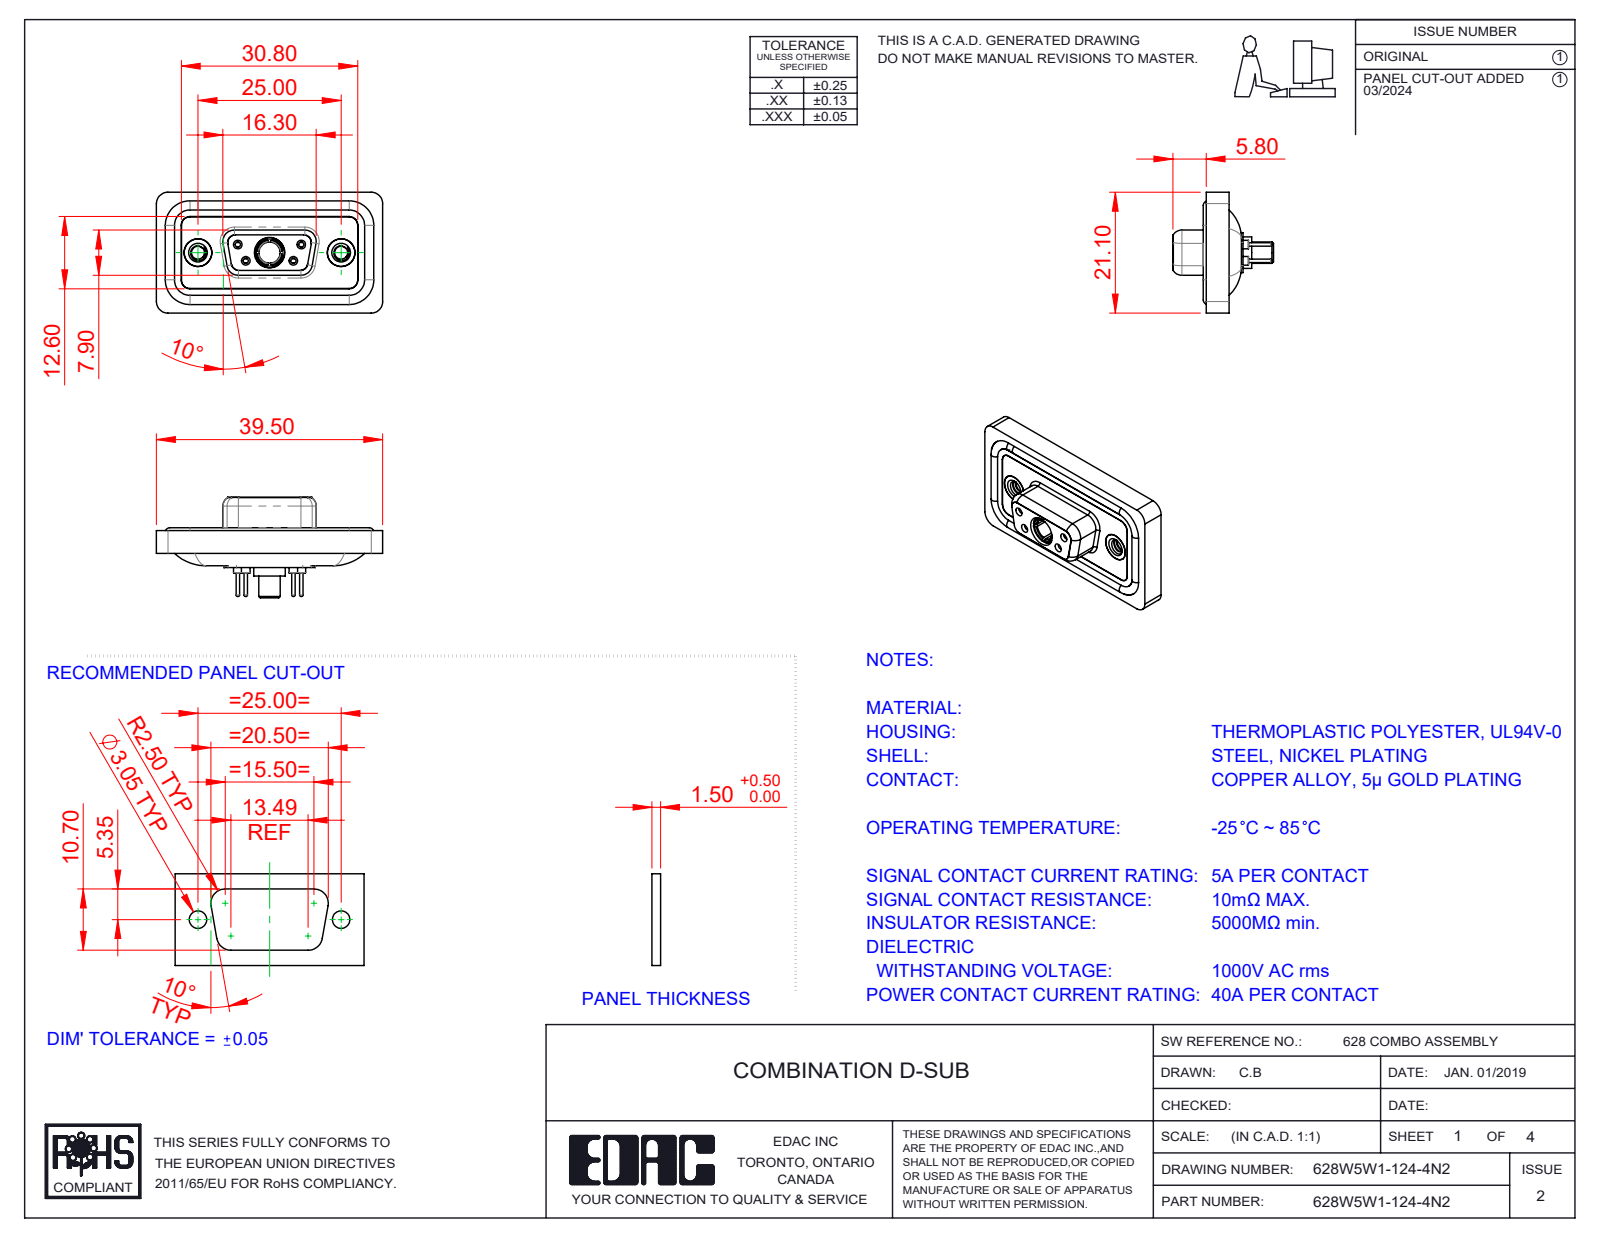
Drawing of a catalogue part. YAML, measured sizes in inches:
part_name: "628W5W1-124-4N2; 628Combo Housing_5W1; 628Combo Waterproof Housing_09 Contacts; 628Combo Contact Row 1_24 (+5 more)"
step_written_by: "SolidWorks 2023 (CONFIG_CONTROL_DESIGN)"
units: inches
bodies: {solids: 13, faces: 680, planar: 194, cylindrical: 287, other: 199}
overall_size: [1.555, 0.831, 0.691]
volume: 0.292
surface_area: 11.85
round_holes:
  - {diameter: 0.035, count: 4}
  - {diameter: 0.043, count: 4}
  - {diameter: 0.059, count: 4}
  - {diameter: 0.079, count: 4}
  - {diameter: 0.191, count: 3}
  - {diameter: 0.063, count: 2}
  - {diameter: 0.067, count: 2}
  - {diameter: 0.089, count: 2}
  - {diameter: 0.157, count: 2}
  - {diameter: 0.159, count: 2}
  - {diameter: 0.197, count: 2}
  - {diameter: 0.146, count: 1}
round_bosses_or_shafts:
  - {diameter: 0.063, count: 6}
  - {diameter: 0.087, count: 4}
  - {diameter: 0.024, count: 4}
  - {diameter: 0.195, count: 2}
  - {diameter: 0.189, count: 2}
  - {diameter: 0.217, count: 1}
  - {diameter: 0.205, count: 1}
  - {diameter: 0.195, count: 1}
partial_cylinders:
  - {radius: 0.059, count: 22}
  - {radius: 0.079, count: 18}
  - {radius: 0.053, count: 8}
  - {radius: 0.063, count: 8}
  - {radius: 0.01, count: 4}
  - {radius: 0.02, count: 4}
  - {radius: 0.024, count: 4}
  - {radius: 0.026, count: 4}
face_to_face_distances: [0.016, 0.114, 0.043, 0.071, 0.063, 0.02, 0.222, 0.293, 0.211, 0.142]
hole_center_spacings: [0.124, 0.225, 0.28, 0.492, 0.713, 0.173, 0.173, 0.327]
